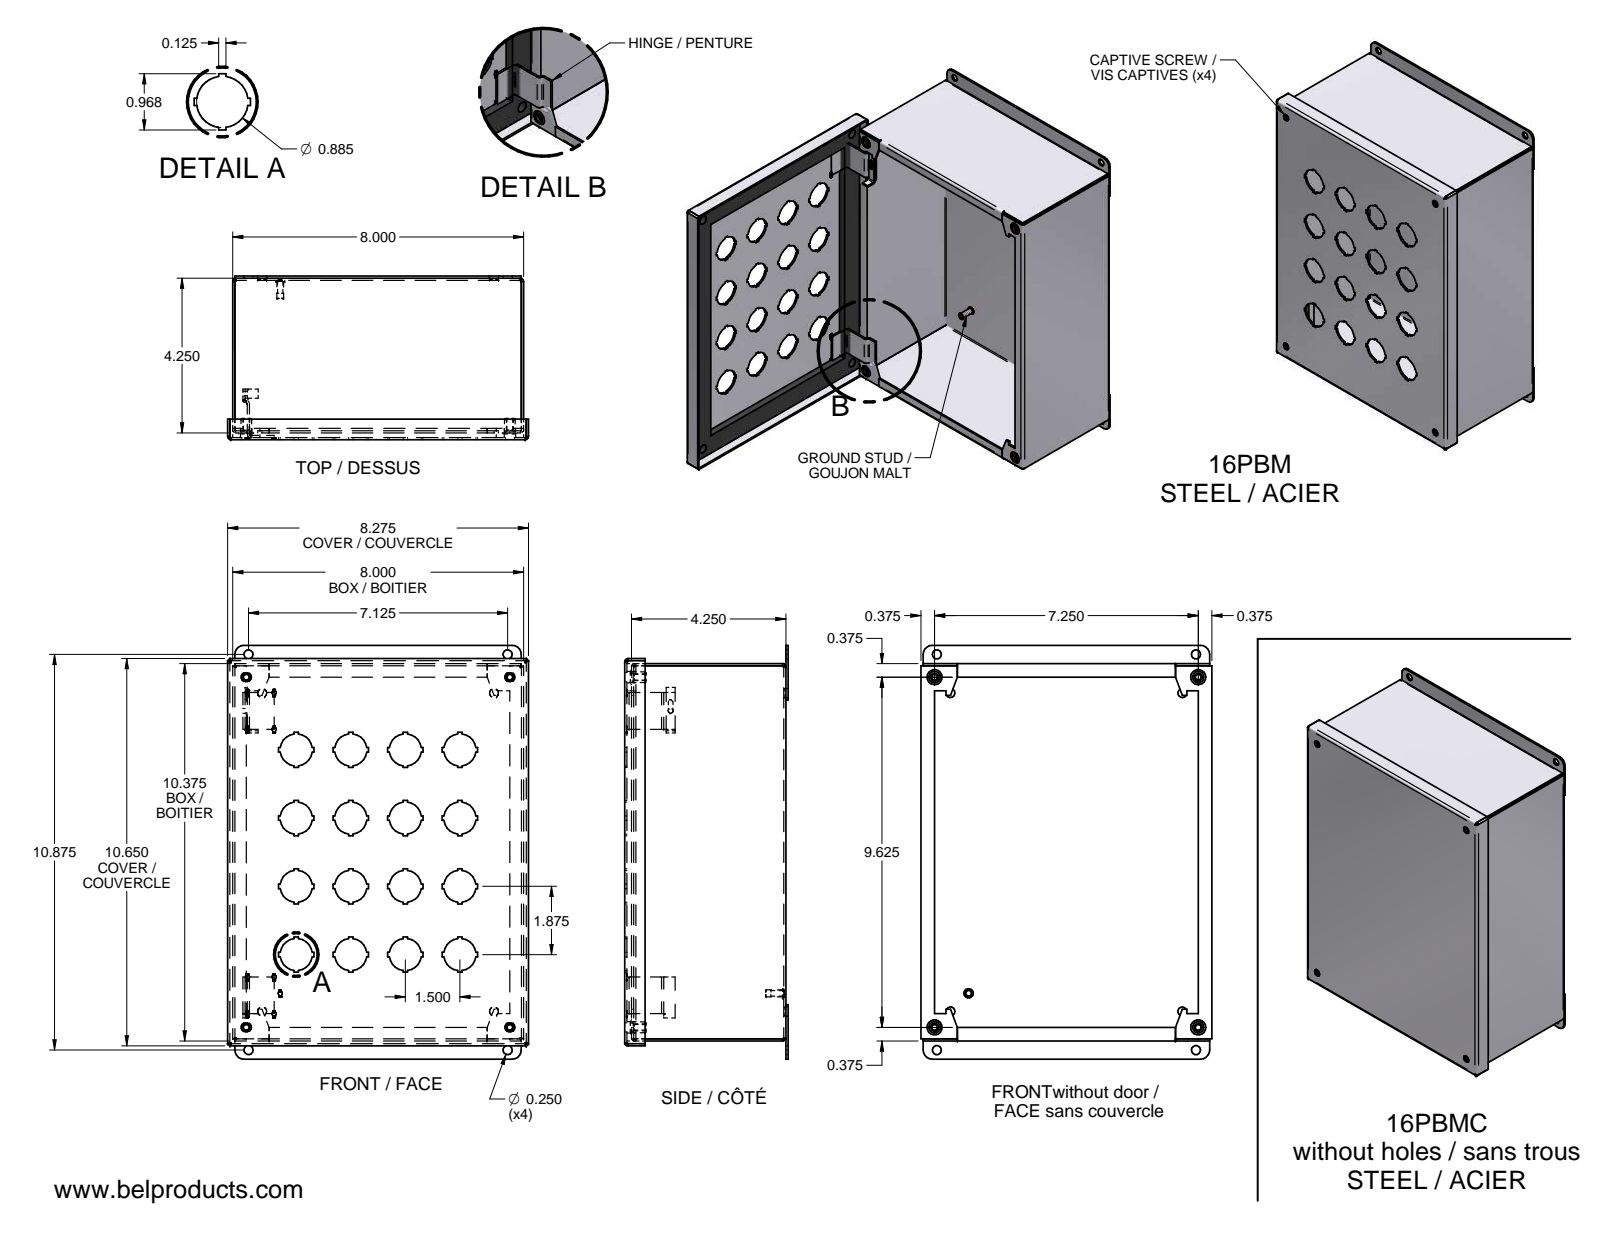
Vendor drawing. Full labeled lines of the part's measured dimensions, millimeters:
Part name (STEP PRODUCT): 16PBMC_COUVERCLE; 16PBMC-C; 16PBMC_GASKET; PB-PENTURE-1 (+7 more)
STEP written by: Unknown (AUTOMOTIVE_DESIGN)
Units: millimetres
Bodies: 13 solids, 1286 faces (899 planar, 106 cylindrical, 281 other)
Overall size (bounding box): 288.93 × 210.19 × 114.17
Volume: 475 808 mm³ · Surface area: 541 371 mm²
Round holes (diameter × count): ⌀3.17 ×9, ⌀6.35 ×8, ⌀4.04 ×4, ⌀5.49 ×4, ⌀6.22 ×4, ⌀6.73 ×4, ⌀7.37 ×4, ⌀7.92 ×4, ⌀3.45 ×1
Round bosses / shafts (diameter × count): ⌀3.02 ×9, ⌀7.52 ×4, ⌀6.35 ×4, ⌀6.5 ×1, ⌀4.83 ×1, ⌀0.51 ×1
Partial cylindrical surfaces — rounded edges, fillets, slot ends (radius × count): R0.81 ×16, R2.34 ×16, R6.35 ×4, R1.59 ×2
Main face-to-face distances: 1.52, 112.65, 111.13, 1.53, 111.12, 201.68, 109.6, 262, 203.2, 200.16
Hole centre spacings: 15.95, 233.62, 260.35, 317.98, 244.48, 15.73, 18.7, 28.62
